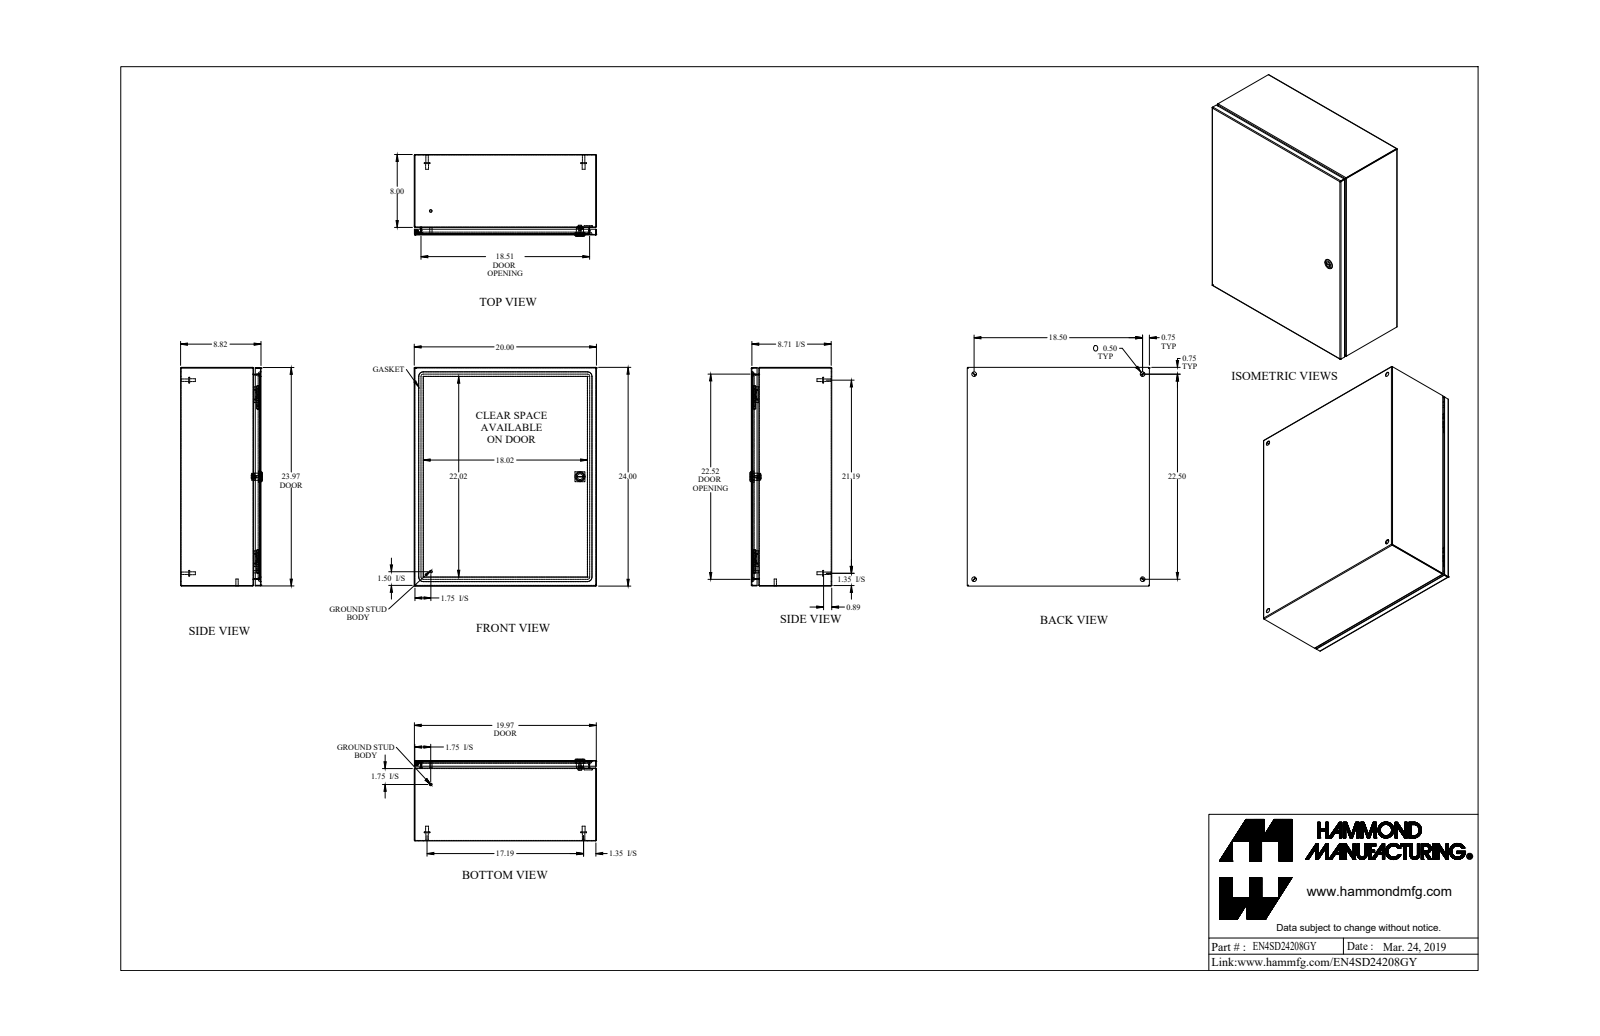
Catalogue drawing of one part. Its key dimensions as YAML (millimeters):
part_name: "EN4SD24208GY_Default"
step_written_by: "SolidWorks 2019 (CONFIG_CONTROL_DESIGN)"
units: millimeters
bodies: {solids: 21, faces: 634, planar: 285, cylindrical: 213, other: 136}
overall_size: [609.6, 508, 228.1]
volume: 1855000
surface_area: 2494000
round_holes:
  - {diameter: 12.7, count: 4}
  - {diameter: 4.4, count: 1}
  - {diameter: 5.9, count: 1}
  - {diameter: 6.1, count: 1}
  - {diameter: 6.1, count: 1}
  - {diameter: 15.9, count: 1}
  - {diameter: 19.9, count: 1}
round_bosses_or_shafts:
  - {diameter: 15.9, count: 4}
  - {diameter: 8, count: 4}
  - {diameter: 6.9, count: 4}
  - {diameter: 7.1, count: 2}
  - {diameter: 6.4, count: 2}
  - {diameter: 27.9, count: 1}
  - {diameter: 13.3, count: 1}
  - {diameter: 11.6, count: 1}
partial_cylinders:
  - {radius: 0.7, count: 21}
  - {radius: 2.2, count: 21}
  - {radius: 6.4, count: 16}
  - {radius: 482.6, count: 8}
  - {radius: 0.2, count: 4}
  - {radius: 1.6, count: 4}
  - {radius: 12.7, count: 4}
  - {radius: 3.2, count: 2}
face_to_face_distances: [1.4, 222.6, 221.2, 224.1, 506.6, 608.2, 505.1, 508, 606.7, 609.6]
hole_center_spacings: [469.9, 571.5, 739.9, 287, 287, 527.2, 527.2]
